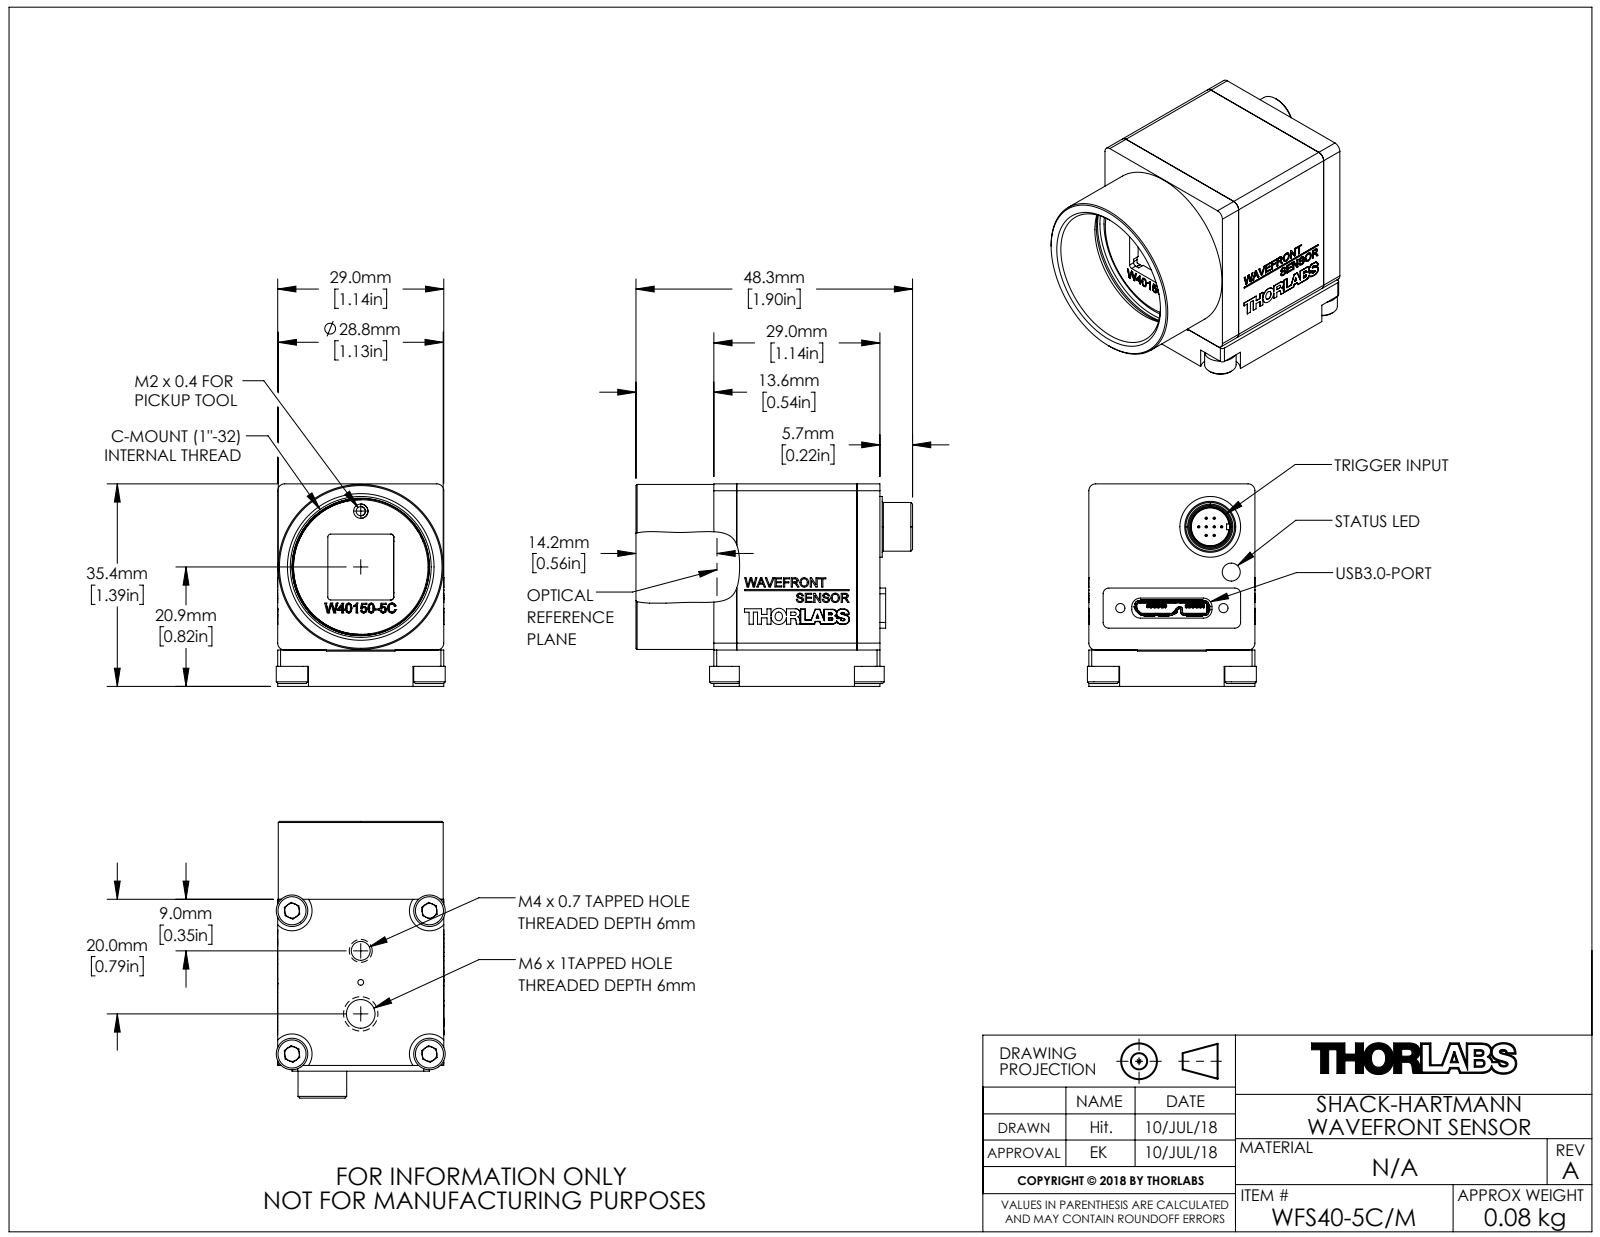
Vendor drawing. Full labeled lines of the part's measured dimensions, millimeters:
Part name (STEP PRODUCT): MTN008539-E0W
STEP written by: SolidWorks 2016 (AUTOMOTIVE_DESIGN)
Units: millimetres
Bodies: 0 solids, 2614 faces (1890 planar, 413 cylindrical, 311 other)
Overall size (bounding box): 48.3 × 35.35 × 29.5
Round holes (diameter × count): ⌀3.2 ×10, ⌀2.5 ×5, ⌀1.6 ×3, ⌀1.9 ×3, ⌀0.95 ×1, ⌀1 ×1, ⌀1.5 ×1, ⌀3.3 ×1, ⌀5 ×1, ⌀6.8 ×1, ⌀8 ×1, ⌀15 ×1
Round bosses / shafts (diameter × count): ⌀0.4 ×8, ⌀1 ×6, ⌀3 ×5, ⌀5.5 ×4, ⌀28.8 ×1, ⌀23.9 ×1, ⌀23.5 ×1, ⌀15.4 ×1
Partial cylindrical surfaces — rounded edges, fillets, slot ends (radius × count): R0.5 ×37, R0.2 ×31, R0.15 ×29, R1 ×15, R0.3 ×12, R1.5 ×10, R0.1 ×8, R0.6 ×8
Main face-to-face distances: 0.6, 29, 28.4, 6.35, 16.65, 35.35, 1.2, 4.8, 27.8, 2.1
Hole centre spacings: 9.75, 16.89, 9.74, 5.05, 13.79, 18.83, 13.89, 17.33
